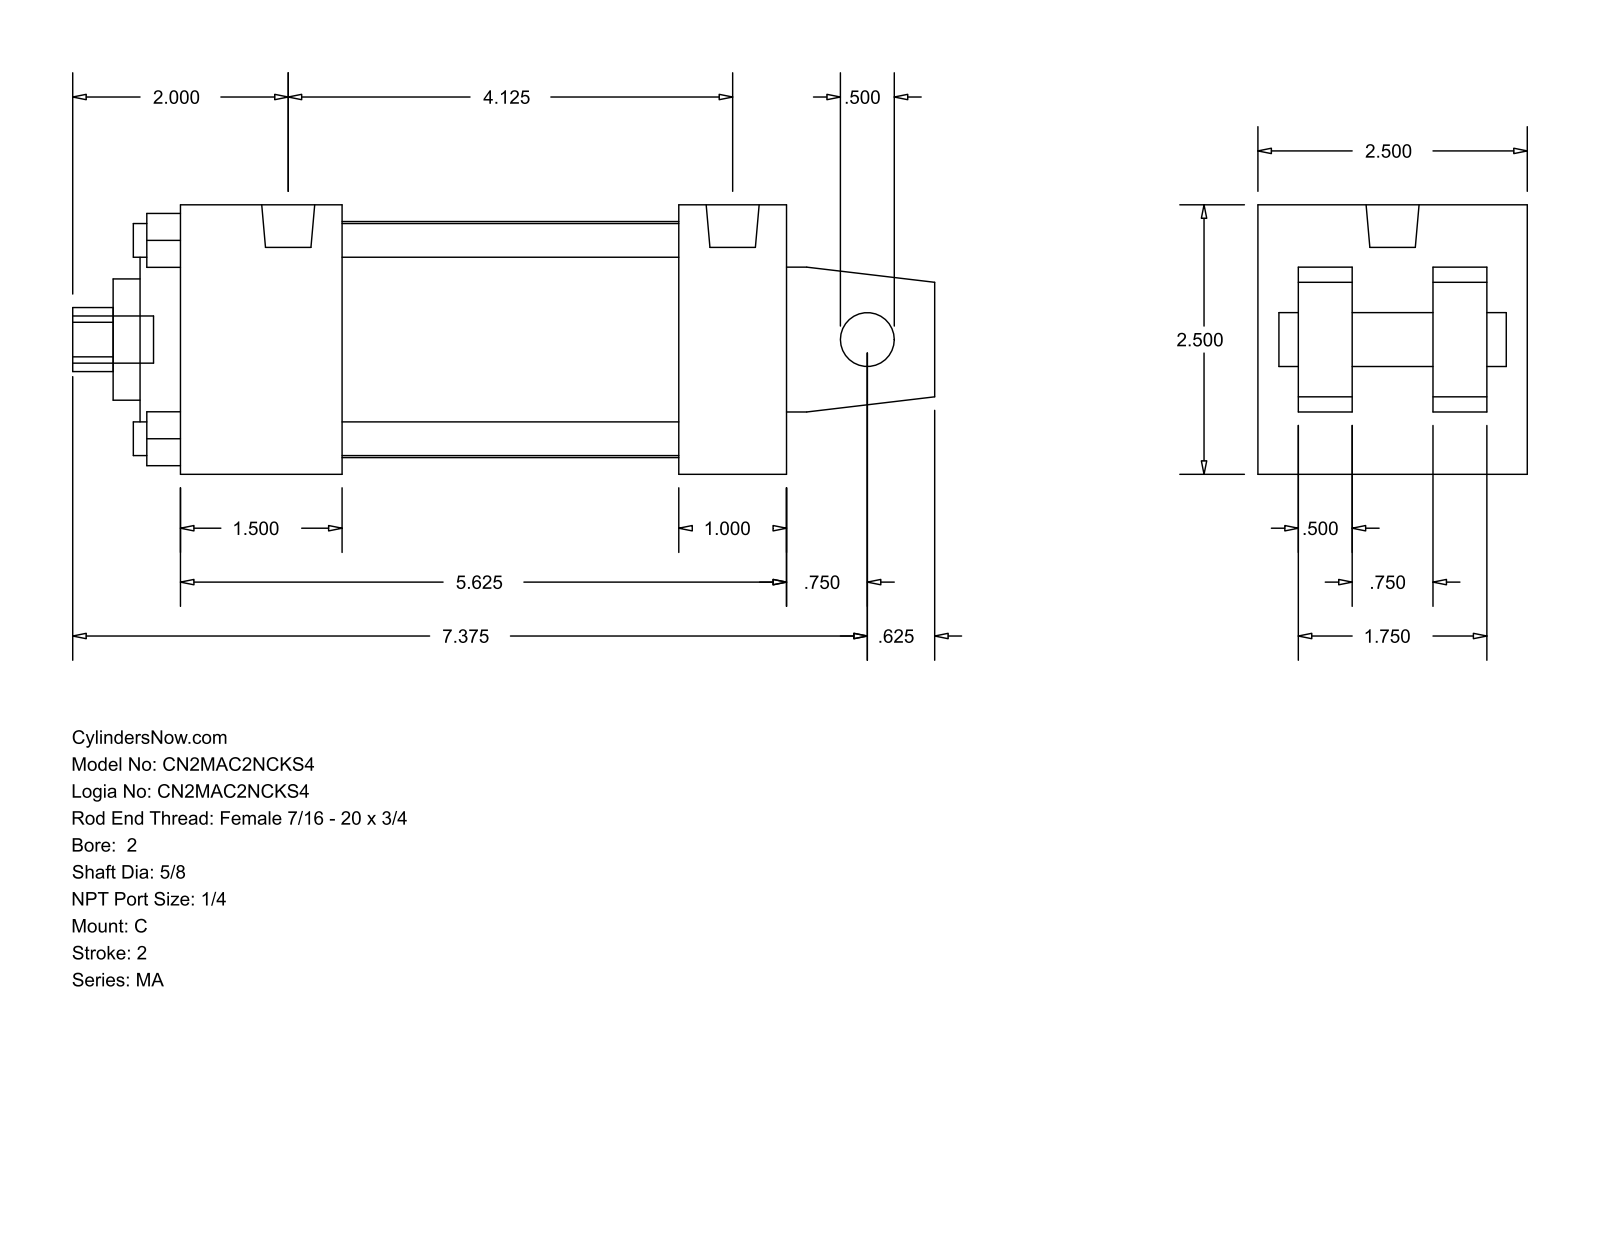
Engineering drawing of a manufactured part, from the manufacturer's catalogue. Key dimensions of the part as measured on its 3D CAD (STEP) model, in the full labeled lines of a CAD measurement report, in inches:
Part name (STEP PRODUCT): MA_C__0200_0.625
STEP written by: GSSL Pune (CONFIG_CONTROL_DESIGN)
Units: inches
Bodies: 0 solids, 105 faces (77 planar, 28 cylindrical, 0 other)
Overall size (bounding box): 8 × 2.5 × 2.5
Round holes (diameter × count): ⌀0.313 ×4, ⌀0.5 ×1, ⌀0.625 ×1, ⌀1.125 ×1, ⌀2 ×1, ⌀2.19 ×1
Round bosses / shafts (diameter × count): ⌀0.313 ×4, ⌀0.492 ×2, ⌀0.437 ×1
Partial cylindrical surfaces — rounded edges, fillets, slot ends (radius × count): R0.297 ×1
Main face-to-face distances: 2.5, 0.375, 0.5, 0.875, 1.625, 2.125, 1.25, 1, 1.5, 5.625
Hole centre spacings: 1.301, 1.84, 2.602
